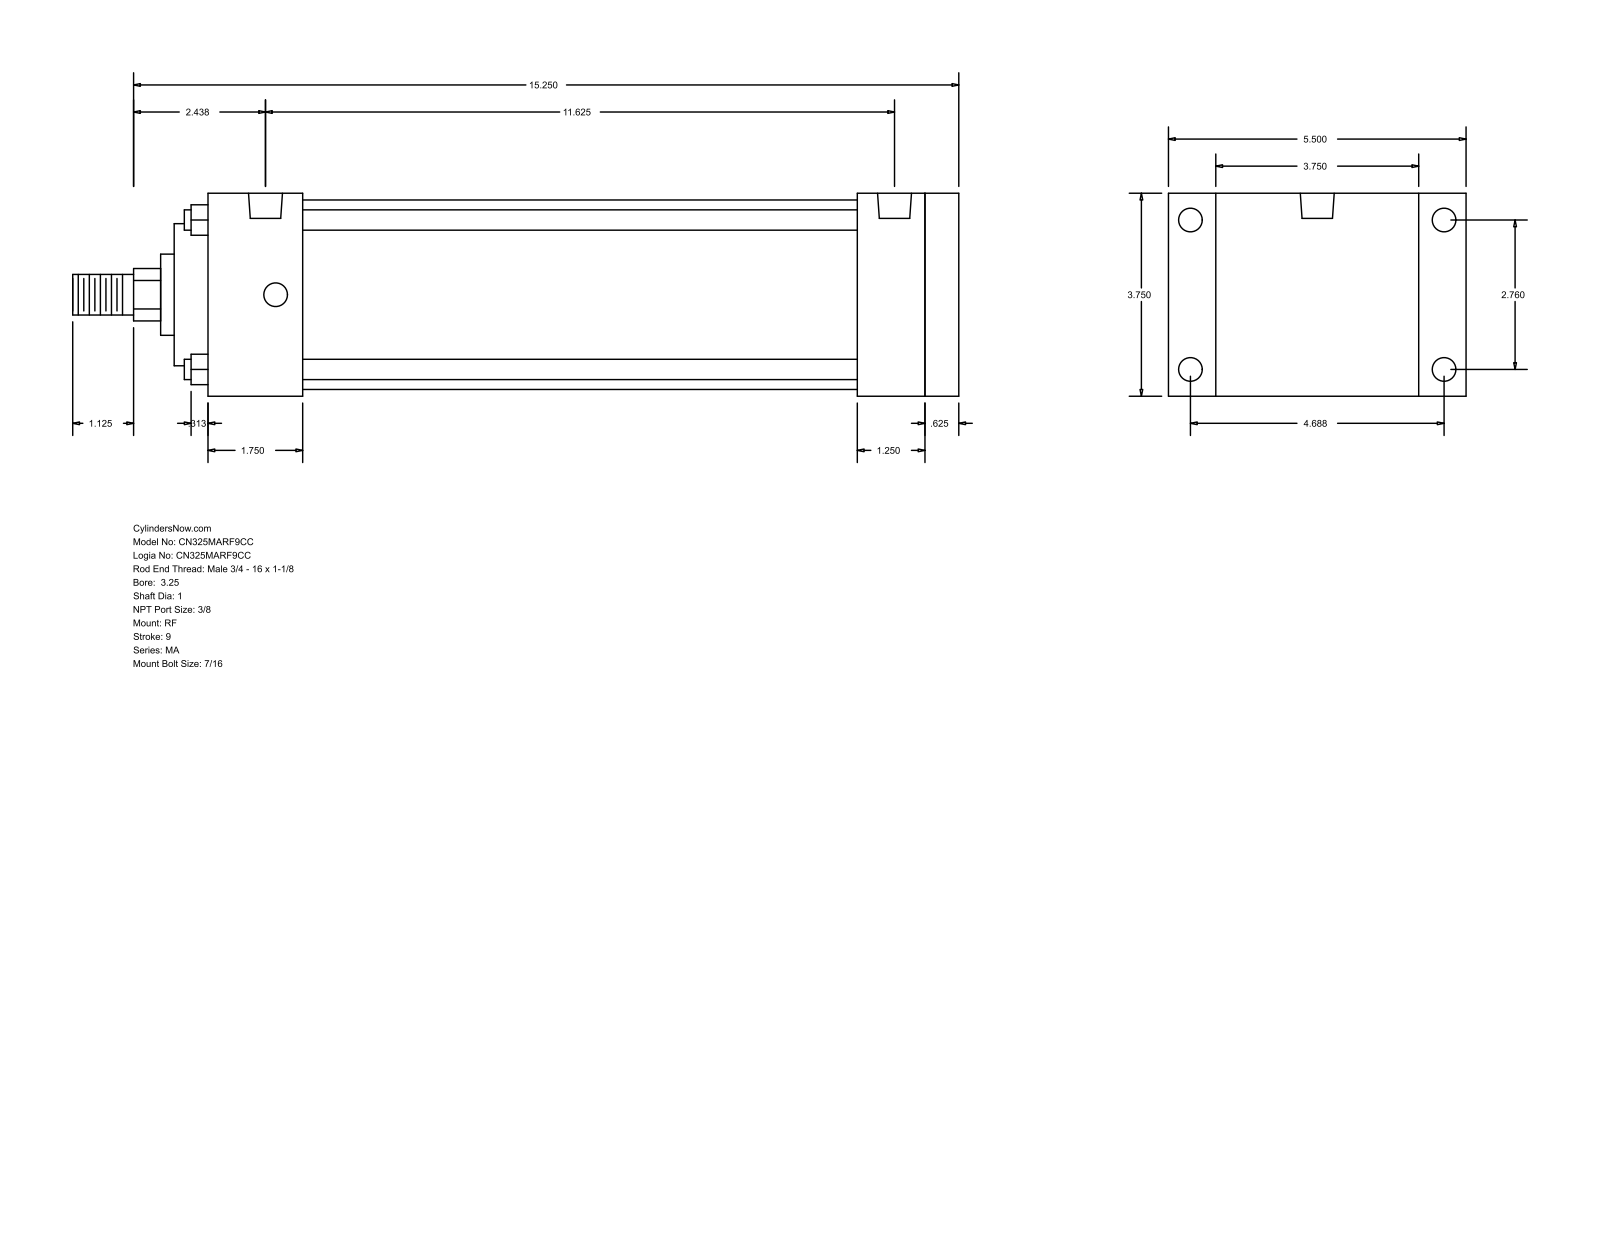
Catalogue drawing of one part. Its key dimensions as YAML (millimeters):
part_name: "MA_RF__0325_1"
step_written_by: "GSSL Pune (CONFIG_CONTROL_DESIGN)"
units: millimeters
bodies: {solids: 0, faces: 94, planar: 65, cylindrical: 29, other: 0}
overall_size: [415.93, 139.7, 95.25]
round_holes:
  - {diameter: 11.11, count: 8}
  - {diameter: 15.93, count: 2}
round_bosses_or_shafts:
  - {diameter: 9.53, count: 4}
  - {diameter: 88.9, count: 1}
  - {diameter: 66.67, count: 1}
  - {diameter: 38.1, count: 1}
  - {diameter: 25.4, count: 1}
  - {diameter: 19.05, count: 1}
partial_cylinders:
  - {radius: 12.29, count: 1}
face_to_face_distances: [95.24, 352.43, 15.87, 336.56, 22.23, 117.47, 47.62, 368.3, 304.81, 31.75]
hole_center_spacings: [4.76, 70.1, 119.06, 138.16, 285.76, 290.52, 295.28]
